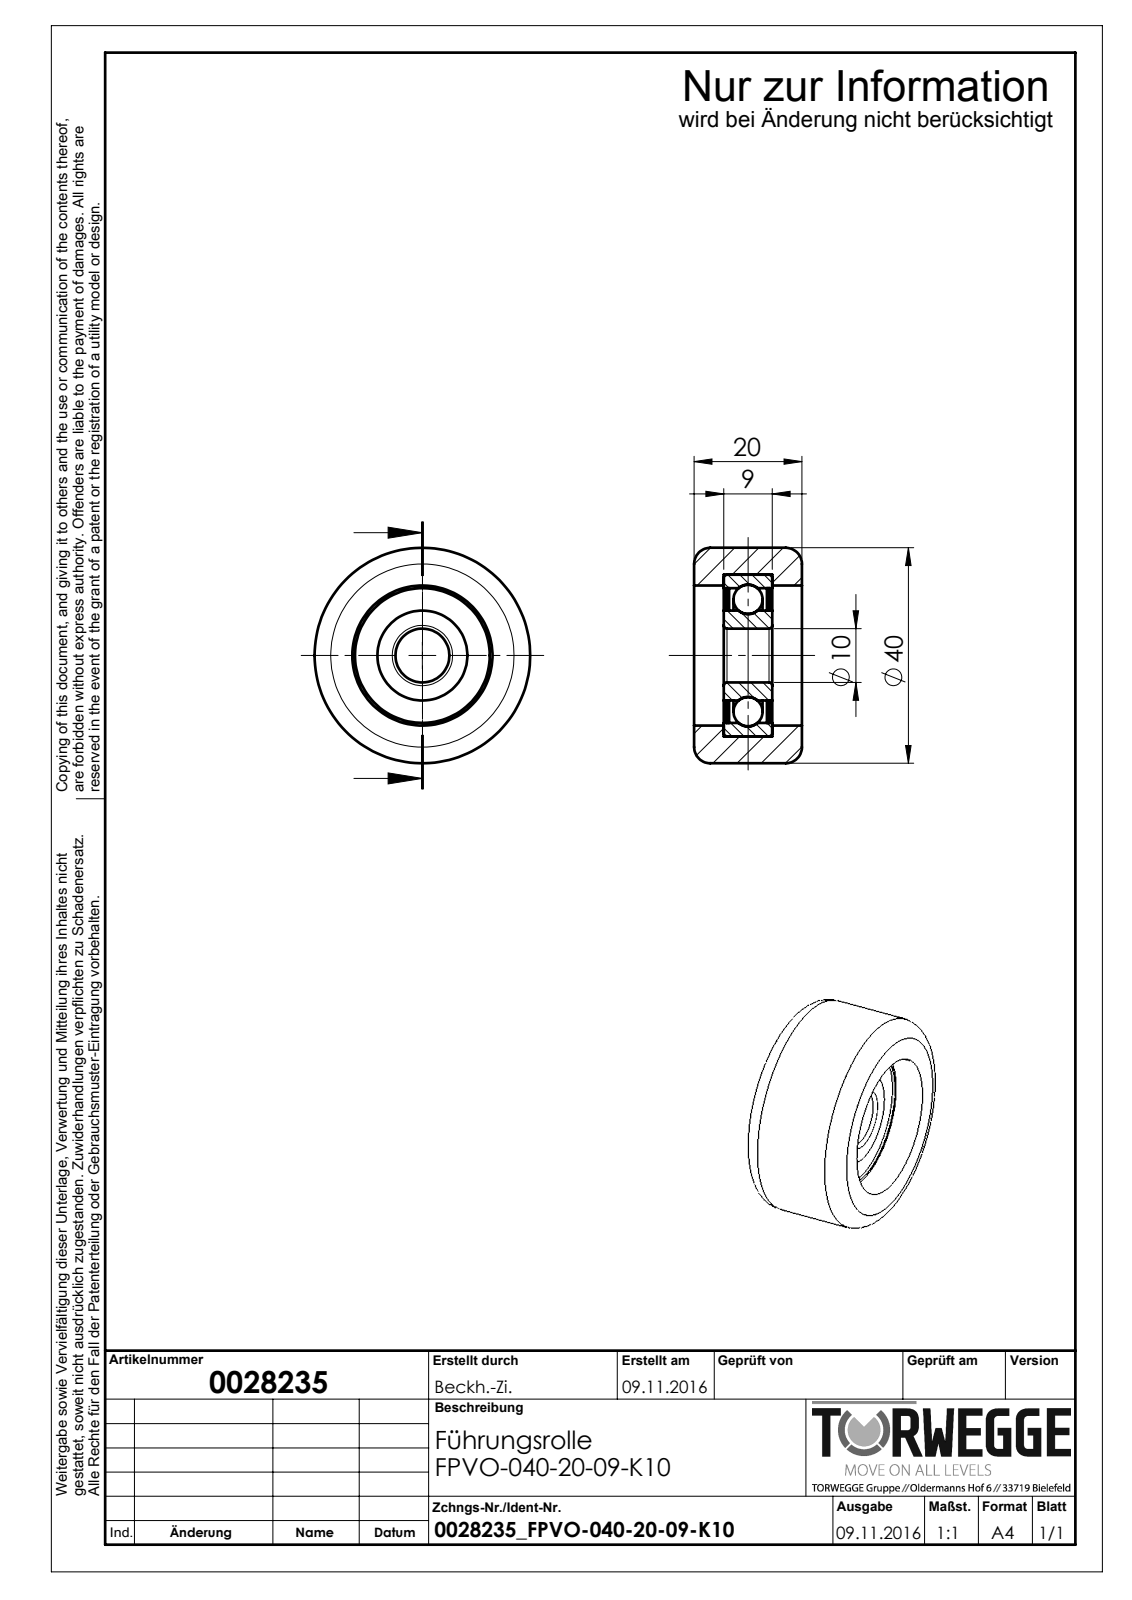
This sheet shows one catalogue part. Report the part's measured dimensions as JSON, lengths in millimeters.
{"part_name": "0028235_FPVO-040-20-09-K10", "step_written_by": "SolidWorks 2016 (AUTOMOTIVE_DESIGN)", "units": "millimeters", "bodies": {"solids": 6, "faces": 62, "planar": 12, "cylindrical": 28, "other": 22}, "overall_size": [40, 40, 20], "volume_mm3": 17204, "surface_area_mm2": 11062, "round_holes": [[10, 1], [16.7, 1], [25, 1], [26, 1], [30, 1]], "round_bosses_or_shafts": [[40, 1]], "face_to_face_distances": [0.5, 8, 5.5, 14.5, 6, 6.5, 13.5, 14, 1, 8.5]}
